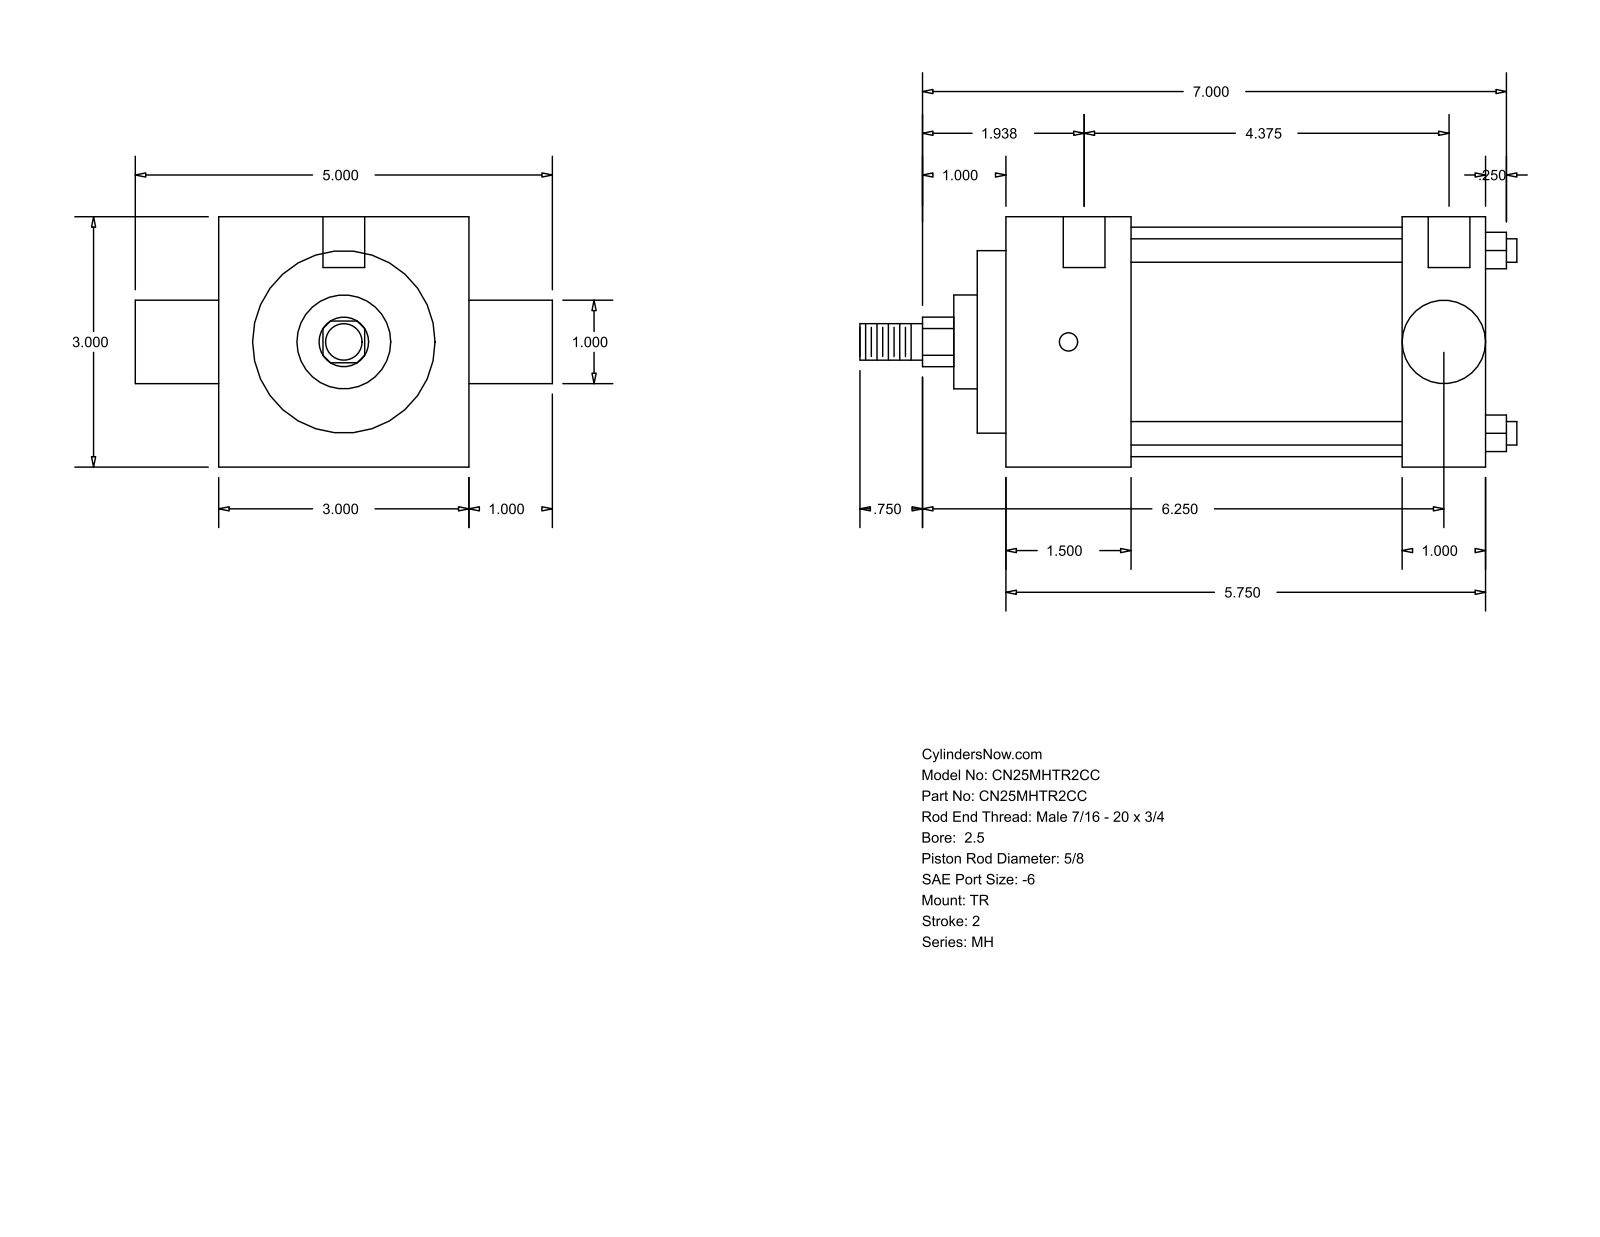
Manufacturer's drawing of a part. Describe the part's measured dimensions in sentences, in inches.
The part is named "MH_TR__0250_0.625". Its 3-D file was written by "GSSL Pune (CONFIG_CONTROL_DESIGN)". It is 0 solids with 86 faces: 61 planar, 25 cylindrical and 0 other. Overall it measures 7.875 by 5 by 3 inches. Round holes: 3 of diameter 0.219, 2 of diameter 0.5. Round bosses or shafts: 4 of diameter 0.281, 1 of diameter 2.75, 1 of diameter 2.187, 1 of diameter 1.125, 1 of diameter 0.998, 1 of diameter 0.625, 1 of diameter 0.437. Partial cylindrical surfaces (rounded edges, fillets, slot ends): 1 of radius 0.297. The main face-to-face distances are 3, 5.75, 1, 3.25, 1.5, 4.25, 4.75, 0.344, 1.844, 5.094. The hole center spacings are 0.125, 0.187, 4.375, 4.5, 4.563, 4.687.
